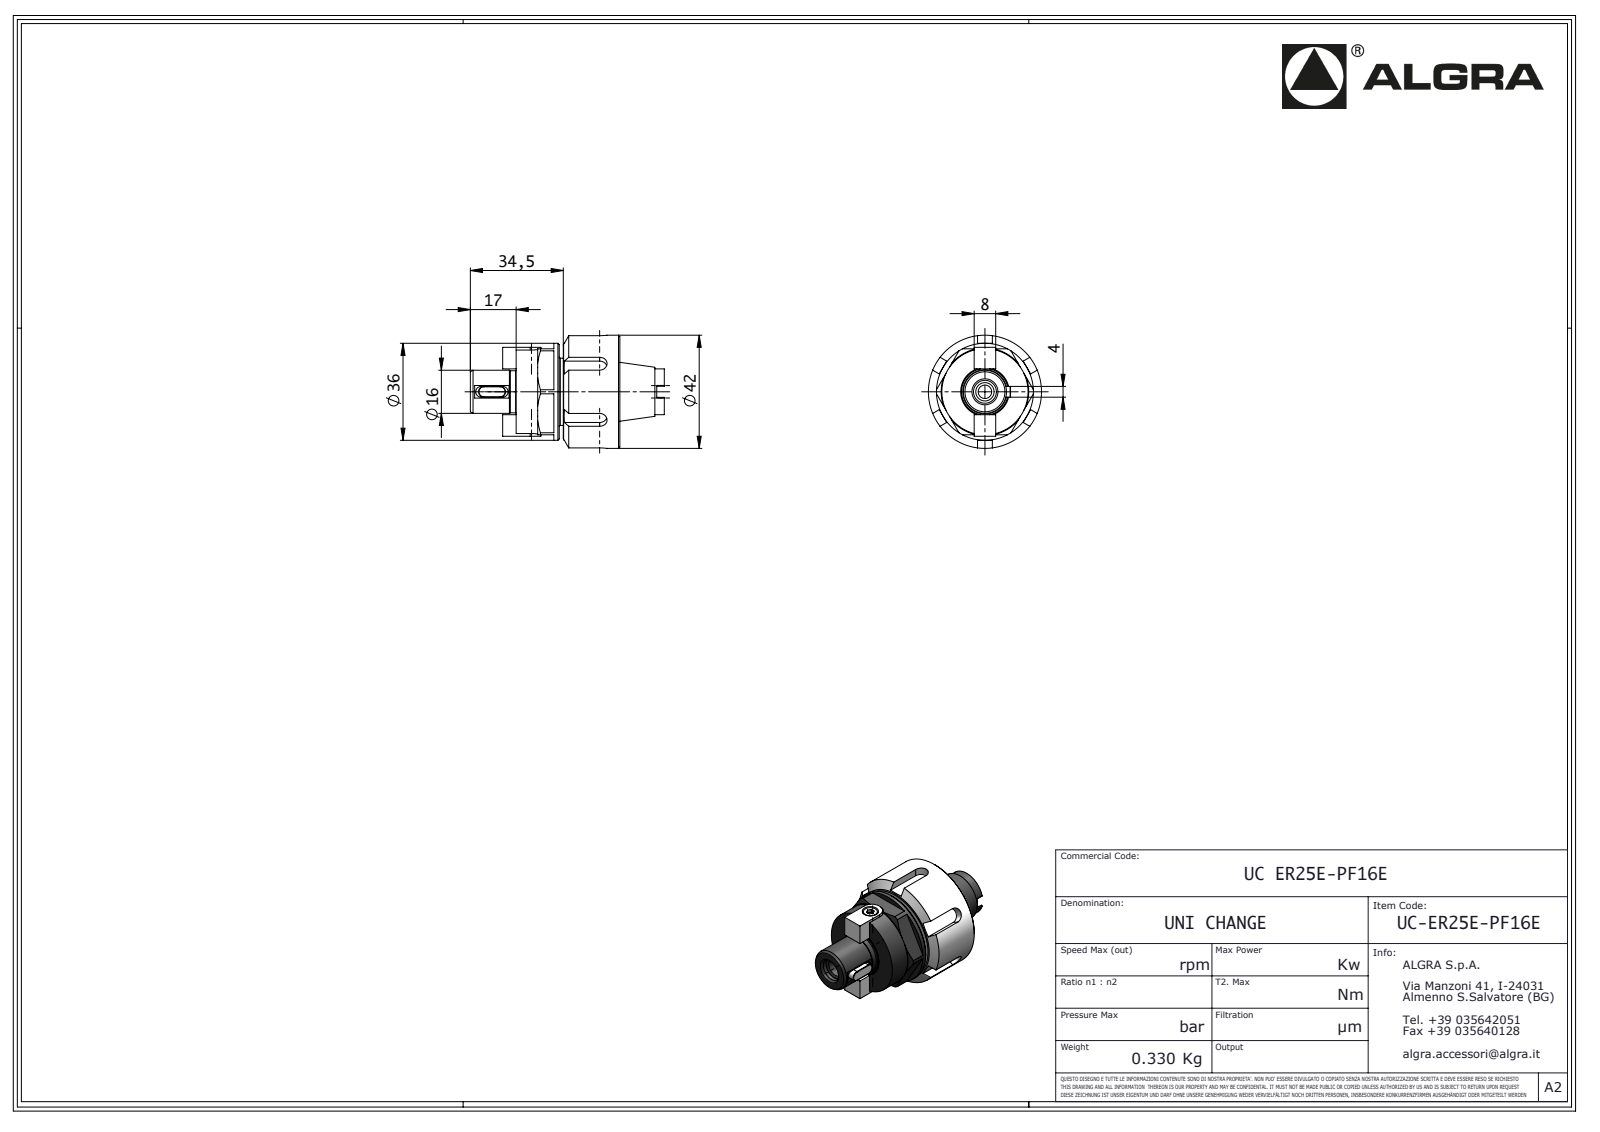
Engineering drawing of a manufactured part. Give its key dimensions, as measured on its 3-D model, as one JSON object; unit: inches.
{"part_name": "UC-ER25E-PF16E", "step_written_by": "SolidWorks 2016 (AUTOMOTIVE_DESIGN)", "units": "inches", "bodies": {"solids": 0, "faces": 166, "planar": 95, "cylindrical": 44, "other": 27}, "overall_size": [2.835, 1.654, 1.654], "round_holes": [[0.098, 2], [0.197, 1], [0.236, 1], [0.268, 1], [0.335, 1], [1.201, 1], [1.276, 1]], "round_bosses_or_shafts": [[1.654, 1], [1.417, 1], [1.26, 1], [0.669, 1], [0.63, 1], [0.614, 1], [0.217, 1]], "partial_cylinders_radius": [[0.009, 4], [0.079, 4], [0.108, 3], [0.006, 2], [0.15, 2], [0.157, 2], [0.199, 1]], "face_to_face_distances": [0.315, 0.886, 0.63, 0.059, 0.081, 1.337, 0.374, 0.827, 1.516, 0.689], "hole_center_spacings": [0.207, 0.413]}
